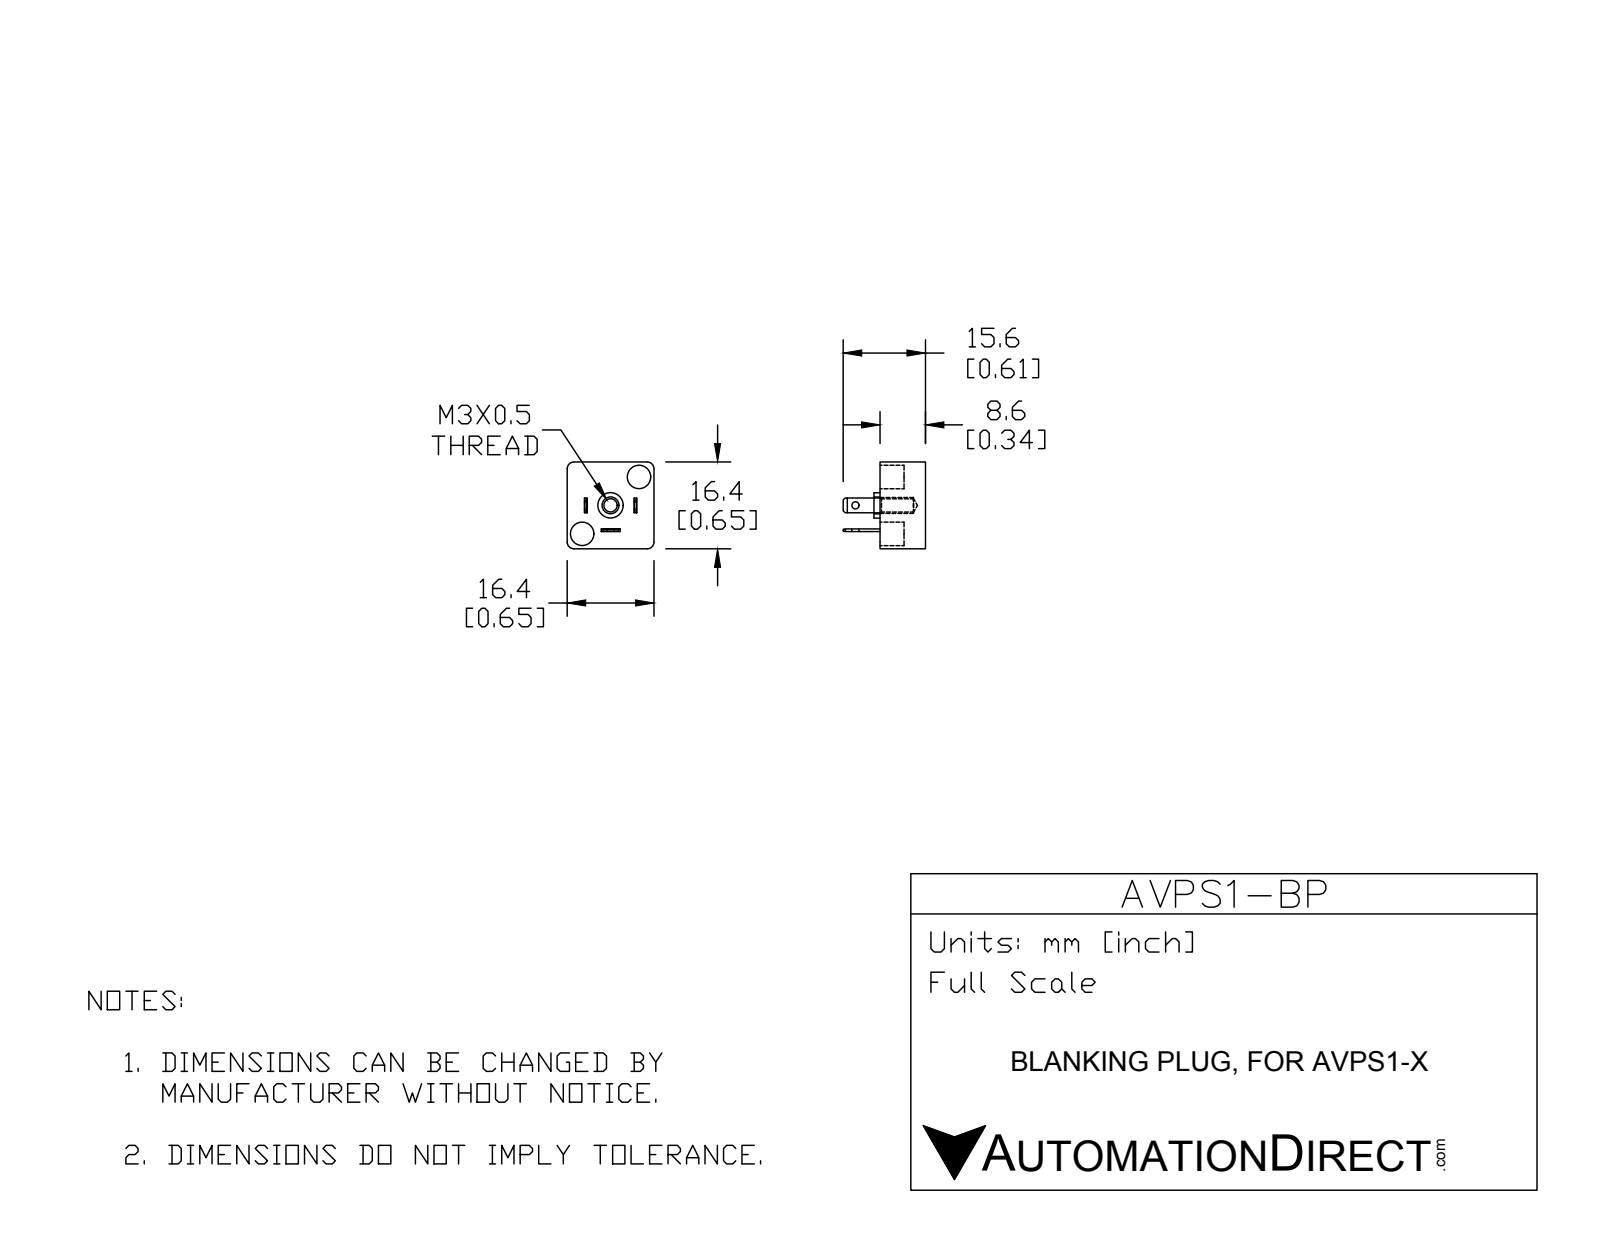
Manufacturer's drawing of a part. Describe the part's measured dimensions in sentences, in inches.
The part is named "AVPS1-BP". Its 3-D file was written by "SolidWorks 2016 (AUTOMOTIVE_DESIGN)". It is 1 solid with 61 faces: 37 planar, 20 cylindrical and 4 other. Overall it measures 0.647 by 0.647 by 0.613 inches. Its volume is 0.133 cubic inches and its surface area 2.222 square inches. Round holes: 2 of diameter 0.053, 2 of diameter 0.175, 1 of diameter 0.098, 1 of diameter 0.126. Round bosses or shafts: 1 of diameter 0.189. Partial cylindrical surfaces (rounded edges, fillets, slot ends): 4 of radius 0.05. The main face-to-face distances are 0.647, 0.339, 0.148, 0.499, 0.129, 0.519, 0.02, 0.37, 0.16, 0.179. The hole center spacings are 0.3, 0.599.
